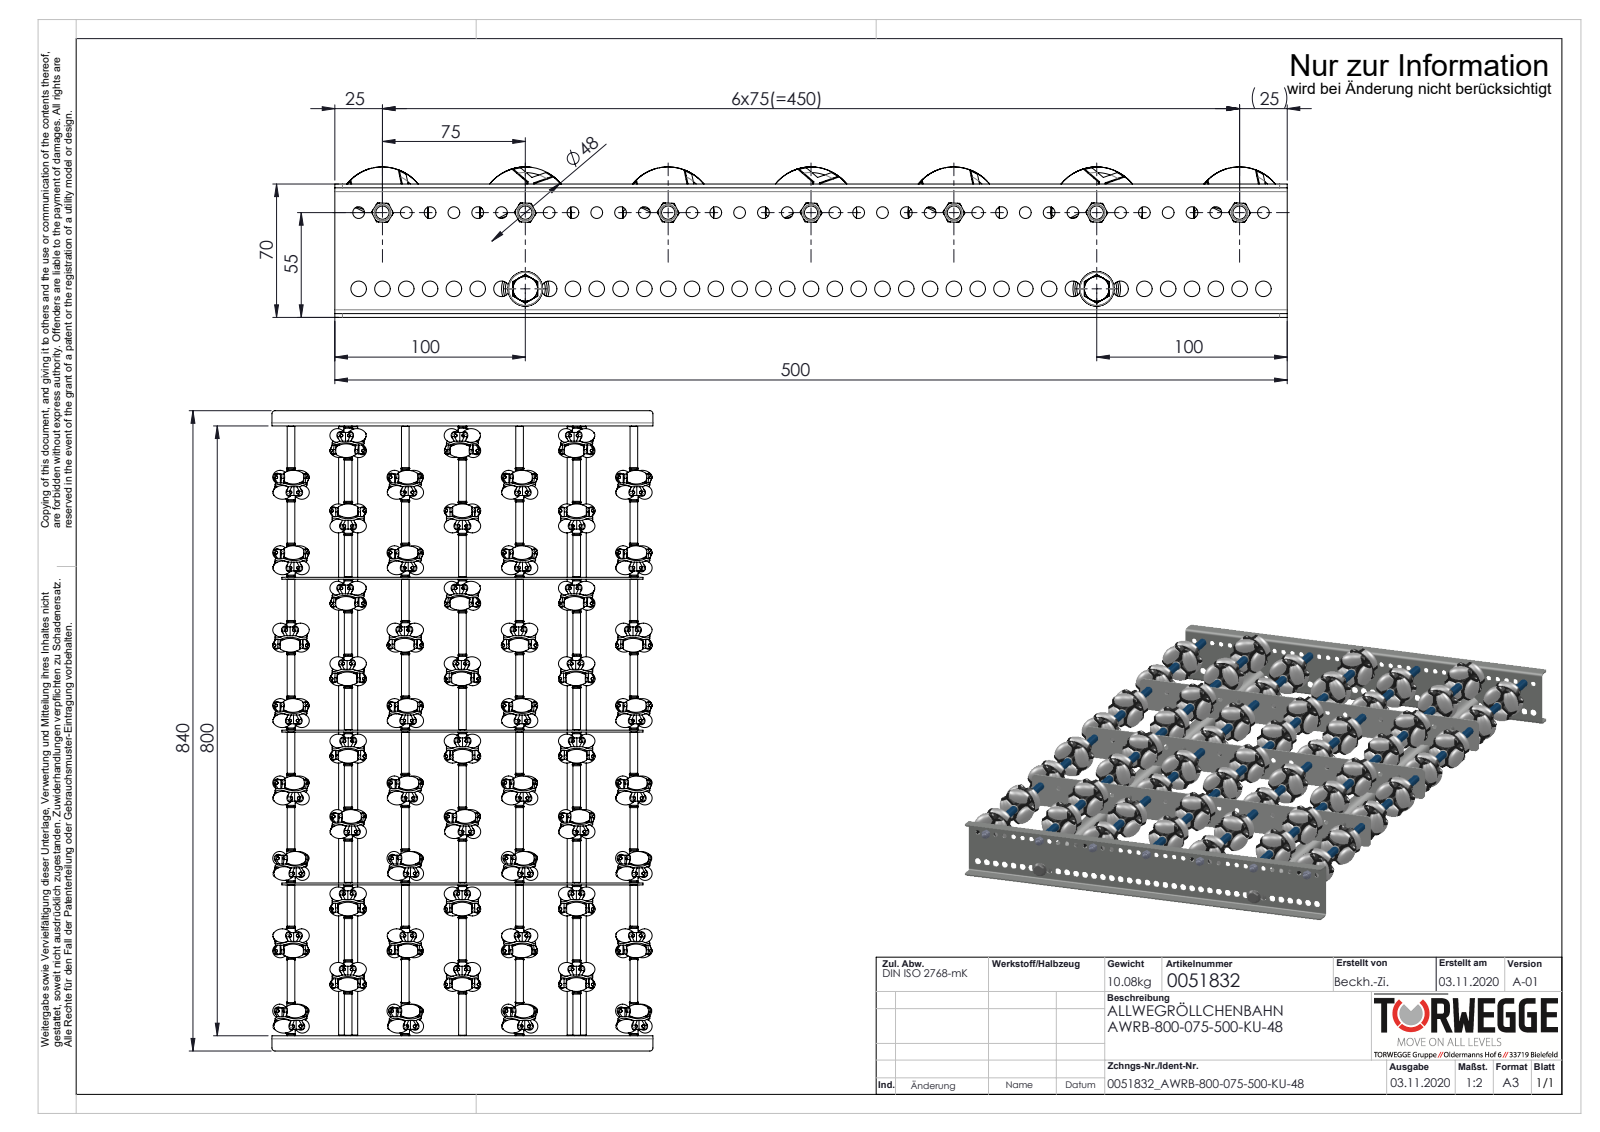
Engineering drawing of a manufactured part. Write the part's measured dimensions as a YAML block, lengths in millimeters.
part_name: "Traversen_KFG_L800; 0015028_AWR48; S100994_Sperrzahnschraube_M08x16-8.8-A2K; AWR48_Halter (+8 more)"
step_written_by: "SolidWorks 2020 (AUTOMOTIVE_DESIGN)"
units: millimeters
bodies: {solids: 932, faces: 16430, planar: 5752, cylindrical: 6388, other: 4290}
overall_size: [840, 500, 79]
volume: 3278000
surface_area: 2262000
round_holes:
  - {diameter: 3.7, count: 336}
  - {diameter: 4.2, count: 336}
  - {diameter: 6.2, count: 39}
  - {diameter: 8.2, count: 39}
  - {diameter: 6.5, count: 19}
  - {diameter: 4.92, count: 7}
  - {diameter: 8.4, count: 7}
  - {diameter: 6.8, count: 2}
  - {diameter: 21, count: 2}
round_bosses_or_shafts:
  - {diameter: 4, count: 336}
  - {diameter: 3.7, count: 275}
  - {diameter: 8, count: 9}
  - {diameter: 47.1, count: 7}
  - {diameter: 42, count: 7}
  - {diameter: 11, count: 7}
  - {diameter: 10, count: 7}
  - {diameter: 7, count: 7}
partial_cylinders:
  - {radius: 4, count: 8}
  - {radius: 2, count: 4}
  - {radius: 5, count: 4}
face_to_face_distances: [2, 200.5, 2.5, 802, 401, 203, 198, 3, 68, 14.75]
hole_center_spacings: [36.05, 36.06, 99, 36.07, 122.72, 36.04, 84.5, 84.51]
